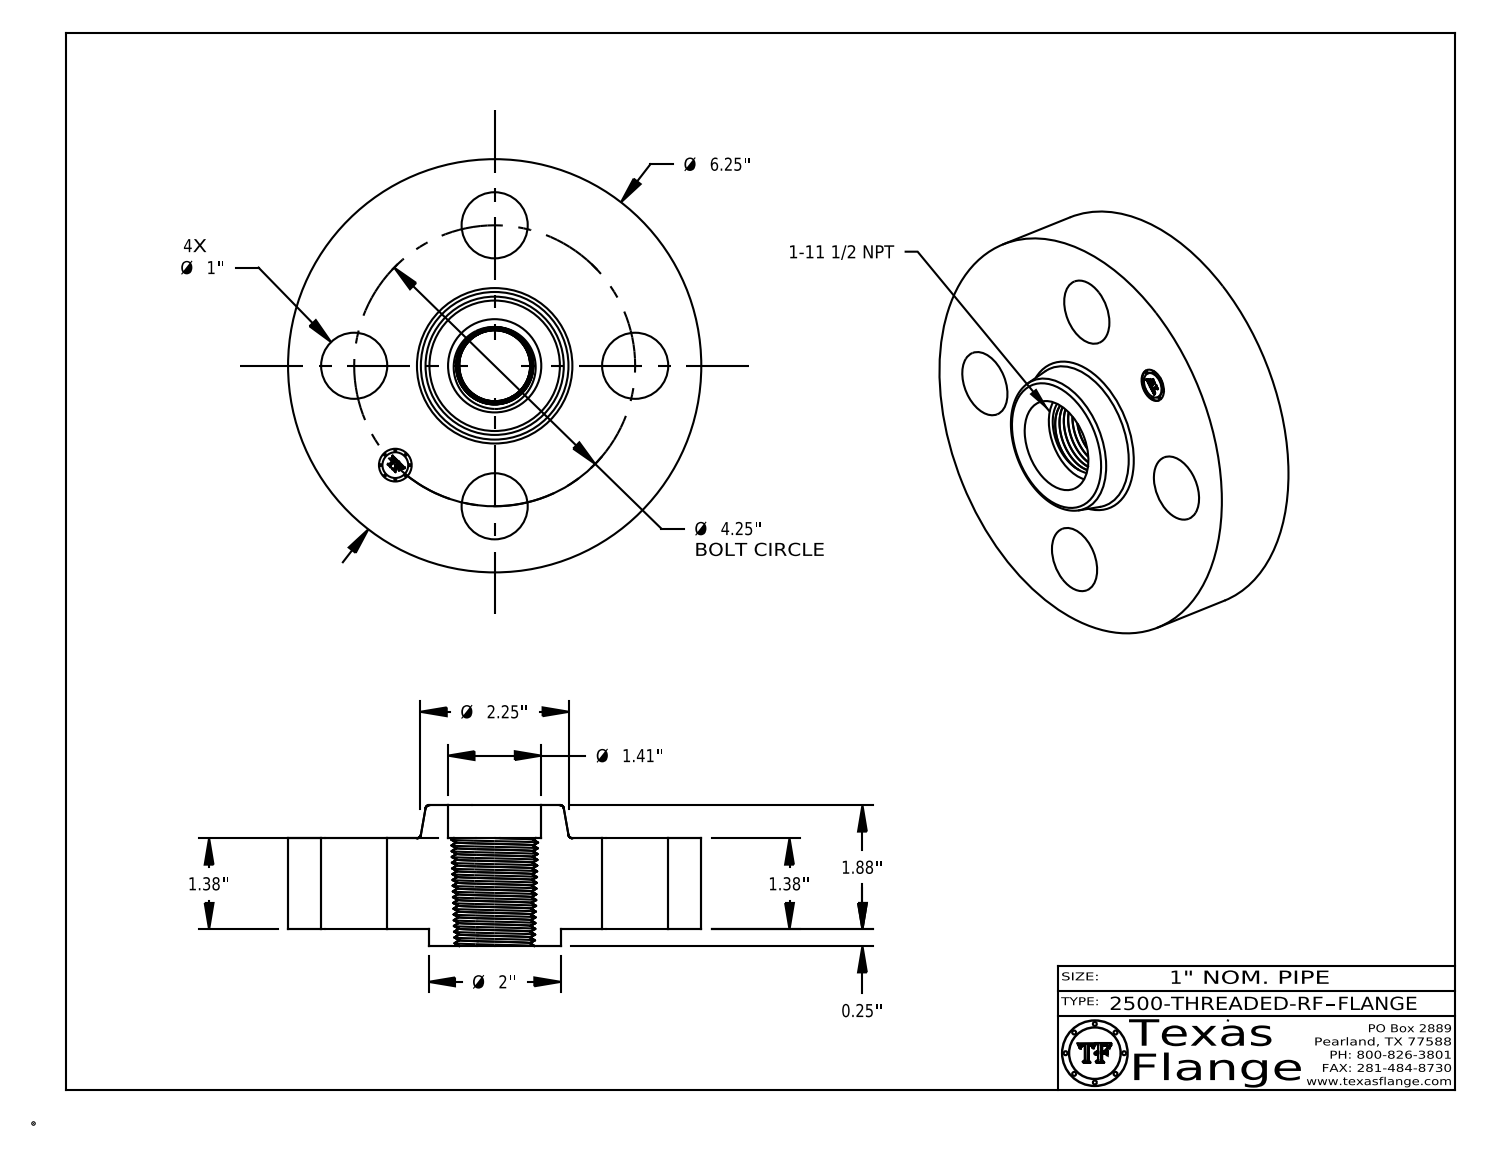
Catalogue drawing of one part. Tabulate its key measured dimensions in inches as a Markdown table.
| quantity | value |
| --- | --- |
| part name | 2500-THREADED-RF |
| STEP written by | CATIA V5 STEP AP214 (AUTOMOTIVE_DESIGN) |
| units | inches |
| bodies | 1 solid, 603 faces (370 planar, 34 cylindrical, 199 other) |
| overall size | 6.25 × 6.25 × 2.13 |
| volume | 38.03 in³ |
| surface area | 115.2 in² |
| round holes (diameter × count) | 1 × 4, 0.495 × 1, 1.41 × 1 |
| round bosses / shafts (diameter × count) | 0.03 × 8, 6.25 × 1, 2 × 1, 0.39 × 1 |
| main face-to-face distances | 1.38, 0.25, 1.63, 2.13, 1.88, 0.5, 1.615, 1.365, 0.015, 0.515 |
| hole center spacings | 2.125, 3.006, 1.626, 3.927, 4.25 |
